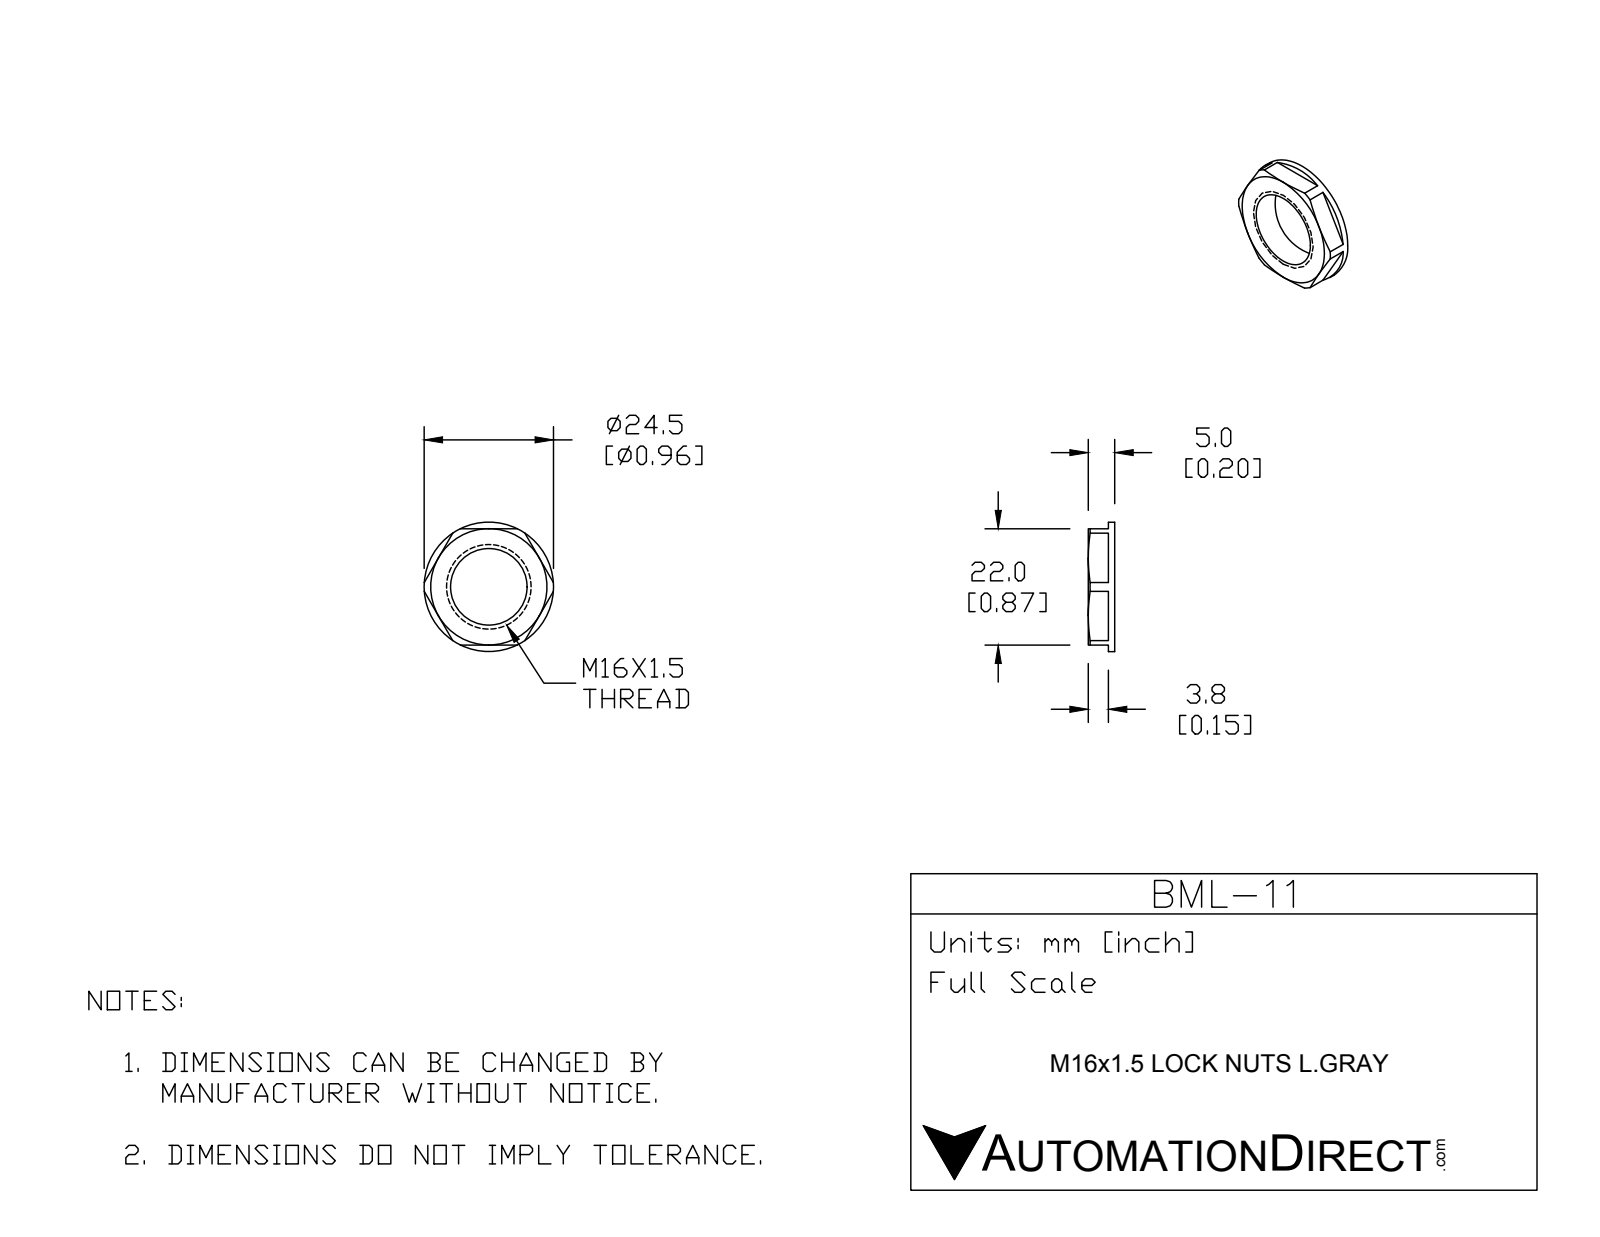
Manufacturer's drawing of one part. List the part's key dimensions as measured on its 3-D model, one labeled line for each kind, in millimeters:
Part name (STEP PRODUCT): BML-11
STEP written by: SolidWorks 2015 (CONFIG_CONTROL_DESIGN)
Units: millimetres
Bodies: 1 solid, 34 faces (17 planar, 10 cylindrical, 7 other)
Overall size (bounding box): 24.5 × 24.5 × 5
Volume: 1 318 mm³ · Surface area: 1 211 mm²
Round holes (diameter × count): ⌀1.5 ×3, ⌀14.5 ×1
Round bosses / shafts (diameter × count): ⌀24.5 ×1
Main face-to-face distances: 5, 22, 1.2, 3.8, 0.9, 4.7
Hole centre spacings: 10.8, 18.7
